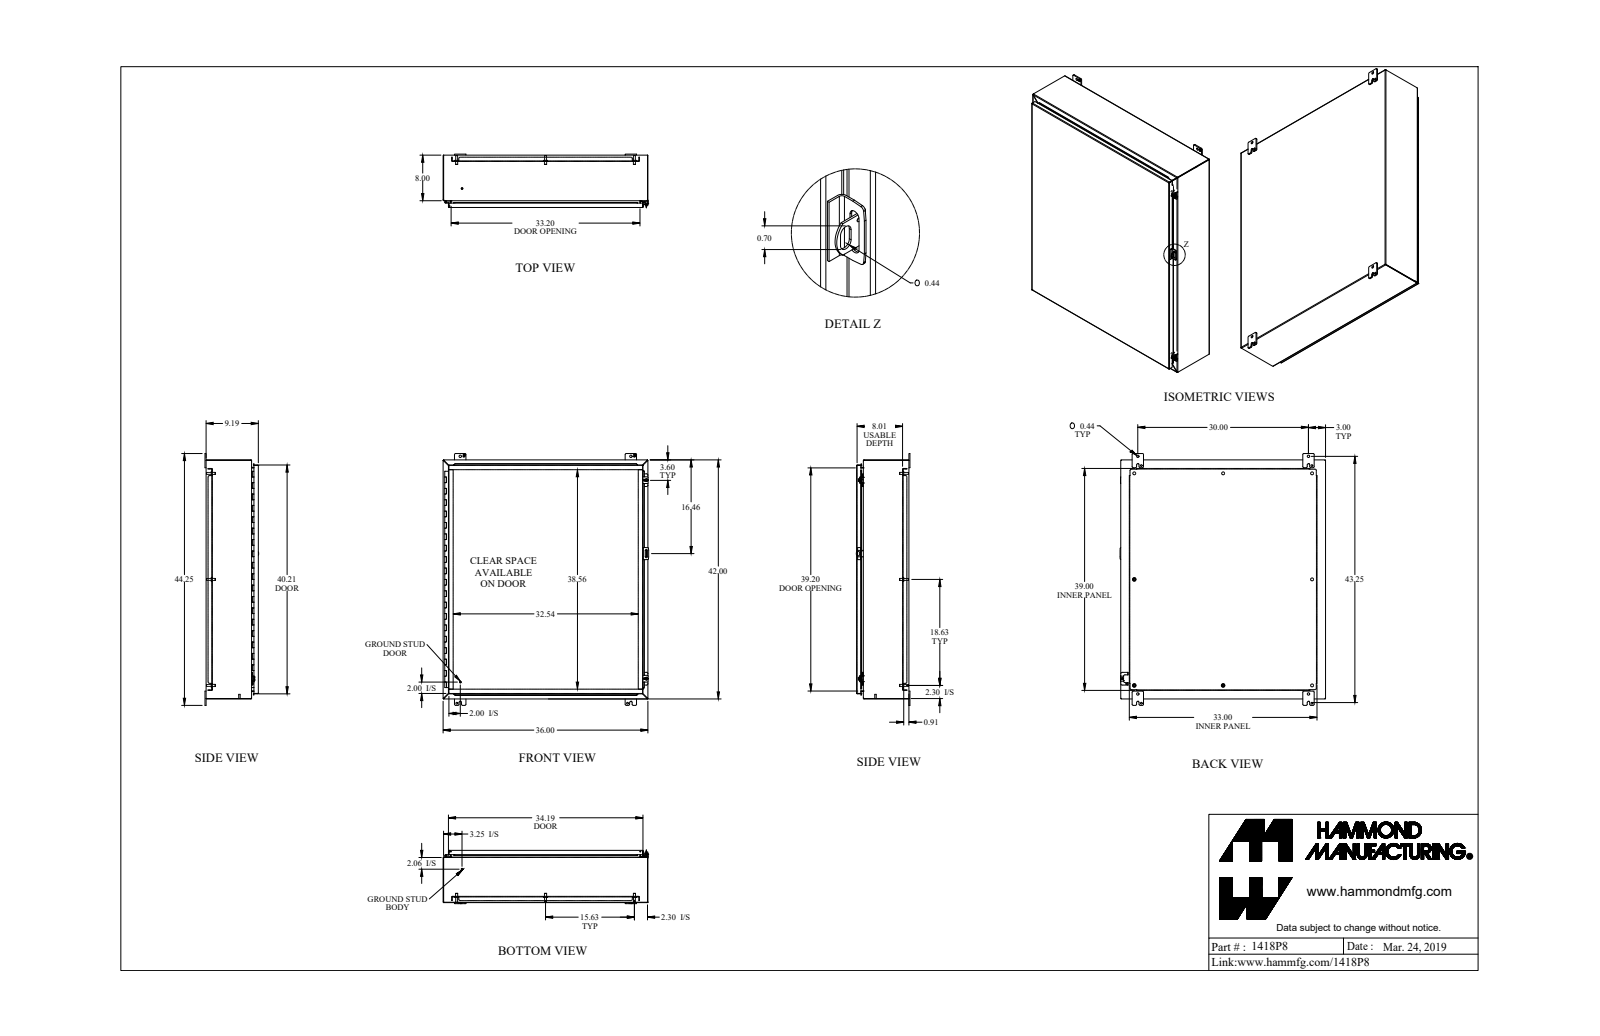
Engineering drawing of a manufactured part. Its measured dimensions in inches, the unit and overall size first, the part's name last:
Units: inches
Overall size (bounding box): 44.25 × 36.125 × 9.437
Round holes (diameter × count): ⌀0.5 ×8, ⌀0.307 ×4, ⌀0.313 ×4, ⌀0.437 ×4, ⌀0.445 ×4, ⌀0.213 ×2, ⌀0.265 ×2, ⌀0.375 ×2, ⌀0.125 ×1, ⌀0.187 ×1
Round bosses / shafts (diameter × count): ⌀0.65 ×8, ⌀0.375 ×8, ⌀0.33 ×8, ⌀1 ×4, ⌀0.5 ×2, ⌀0.39 ×2, ⌀0.281 ×2, ⌀0.25 ×2
Partial cylindrical surfaces — rounded edges, fillets, slot ends (radius × count): R0.188 ×38, R0.036 ×24, R0.108 ×24, R0.25 ×20, R0.116 ×16, R0.048 ×13, R0.143 ×13, R0.04 ×8
Main face-to-face distances: 0.072, 9.113, 9.041, 9.185, 0.095, 0.937, 1.009, 8.081, 8.009, 1.032
Hole centre spacings: 37.25, 15.625, 30, 40.394, 40.394, 48.622, 1.735, 2.434
Volume: 526.1 in³ · Surface area: 13 600 in²
Bodies: 50 solids, 1563 faces (891 planar, 563 cylindrical, 109 other)
Part name (STEP PRODUCT): 1418P8_Default
STEP written by: SolidWorks 2019 (CONFIG_CONTROL_DESIGN)
